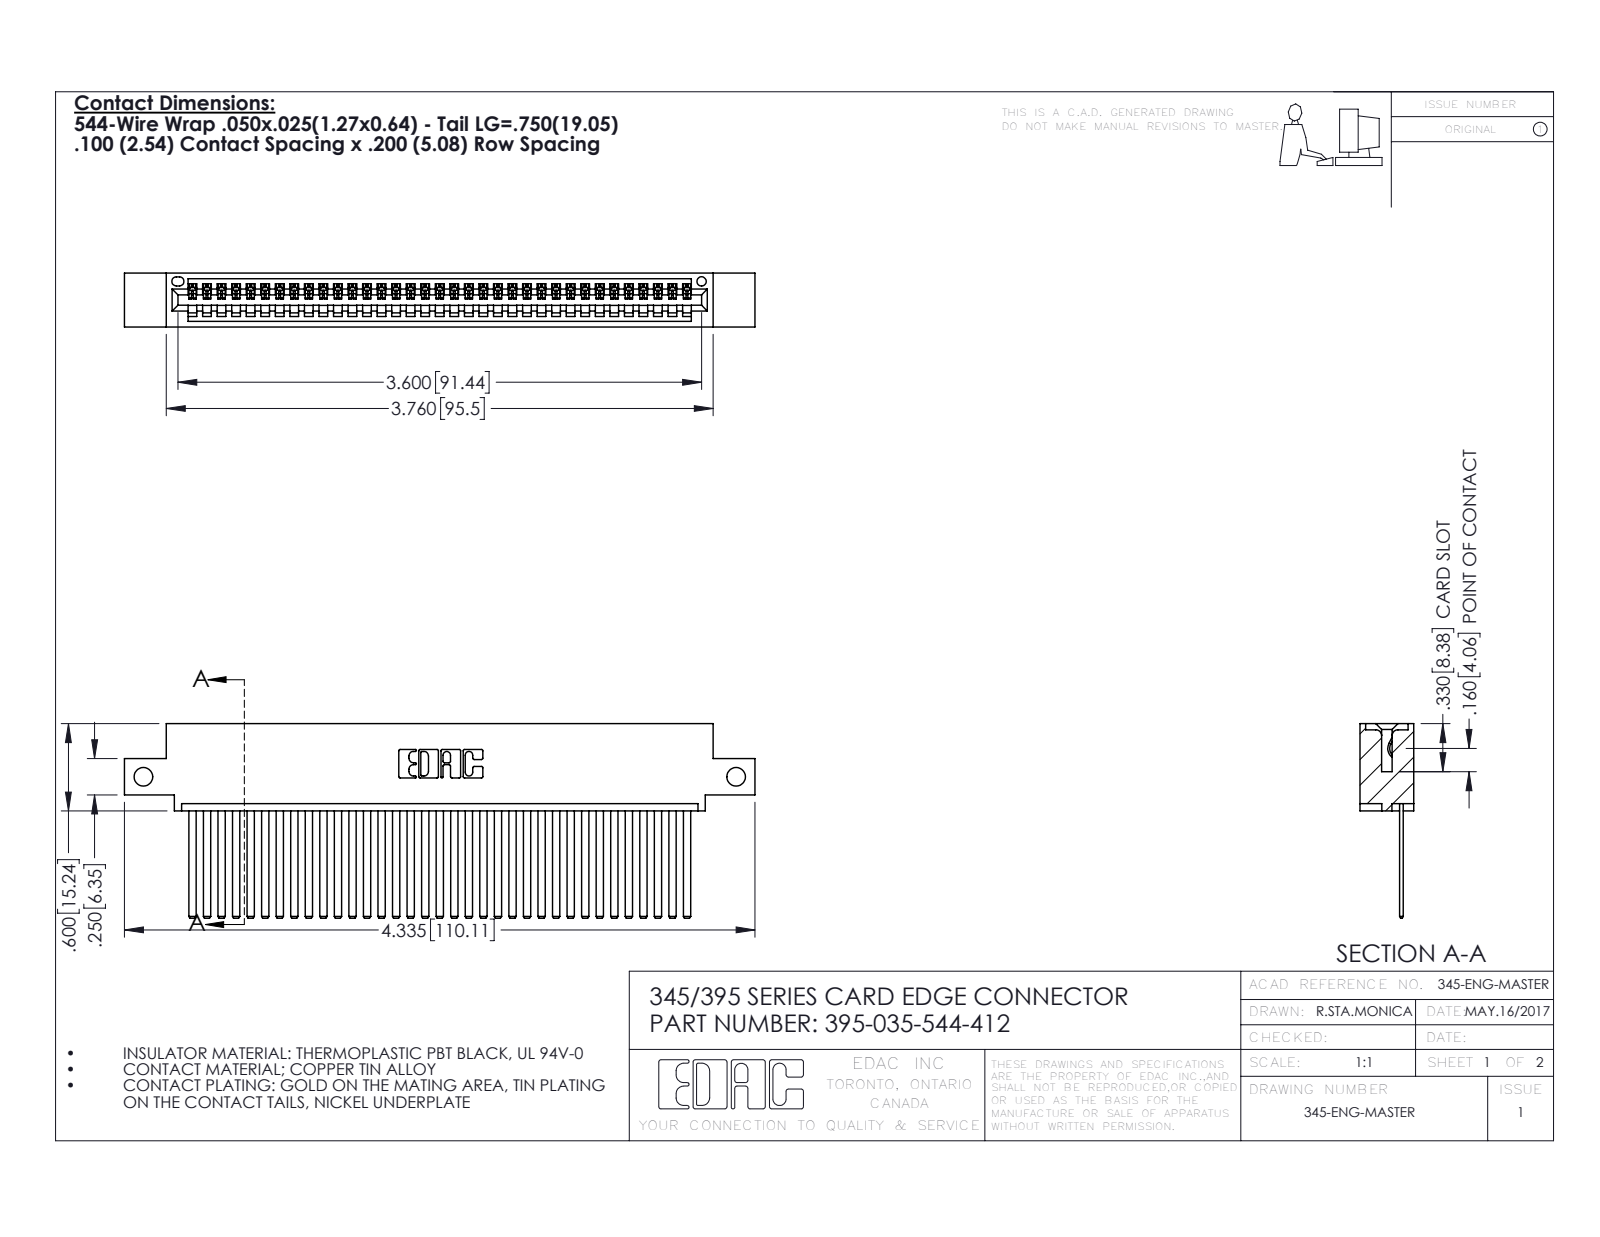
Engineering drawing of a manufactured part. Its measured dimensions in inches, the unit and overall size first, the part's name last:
Units: inches
Overall size (bounding box): 4.335 × 1.337 × 0.37
Round holes (diameter × count): ⌀0.128 ×2, ⌀0.064 ×1
Partial cylindrical surfaces — rounded edges, fillets, slot ends (radius × count): R0.006 ×70, R0.01 ×22, R0.007 ×6, R0.031 ×6, R0.026 ×3, R0.031 ×2, R0.04 ×2, R0.014 ×1
Main face-to-face distances: 0.072, 0.298, 0.025, 0.098, 0.272, 0.37, 0.2, 0.225, 0.149, 0.072
Hole centre spacings: 4.075
Volume: 0.65 in³ · Surface area: 23.57 in²
Bodies: 36 solids, 1950 faces (1344 planar, 606 cylindrical, 0 other)
Part name (STEP PRODUCT): 345-292-001_345-293-144; 345 Part_0.110 Offset - Side Mount; 395-035-544-412
STEP written by: SolidWorks 2016 (CONFIG_CONTROL_DESIGN)
